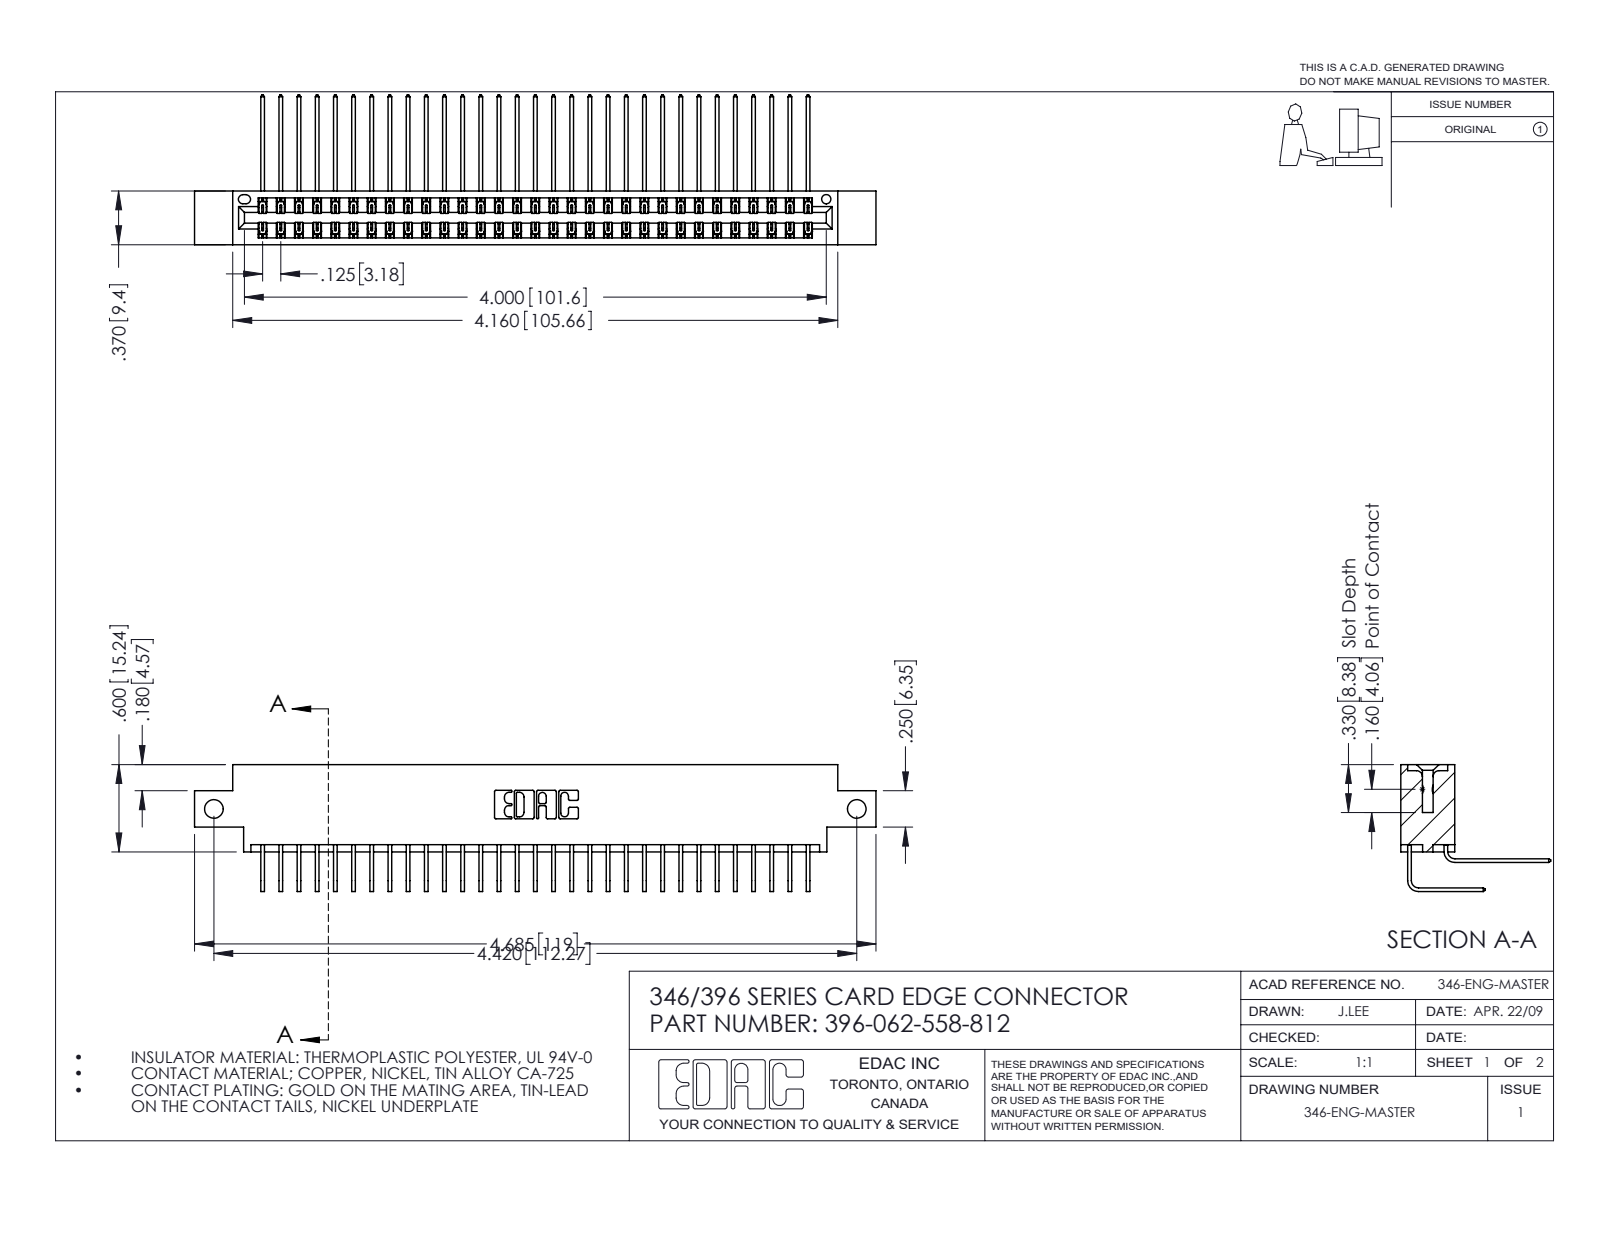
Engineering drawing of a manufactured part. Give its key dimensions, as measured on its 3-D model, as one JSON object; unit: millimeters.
{"part_name": "345-292-001_558 Tail - 2; 345-292-001_558 559 Tail - 1; 396-062-558-812; 346 Part_0.170 Offset - Side Mount", "step_written_by": "SolidWorks 2016 (CONFIG_CONTROL_DESIGN)", "units": "millimeters", "bodies": {"solids": 63, "faces": 3474, "planar": 2374, "cylindrical": 1100, "other": 0}, "overall_size": [119, 26.2, 22.2], "volume_mm3": 11600, "surface_area_mm2": 17570, "round_holes": [[3.3, 2], [1.6, 1]], "partial_cylinders_radius": [[0.2, 93], [0.3, 22], [0.2, 6], [0.8, 6], [0.7, 3], [0.4, 2], [0.6, 2], [0.6, 2]], "face_to_face_distances": [8.2, 1.2, 0.6, 9.4, 6.4, 7.6, 1.8, 7, 3.8, 5.6], "hole_center_spacings": [112.3]}
